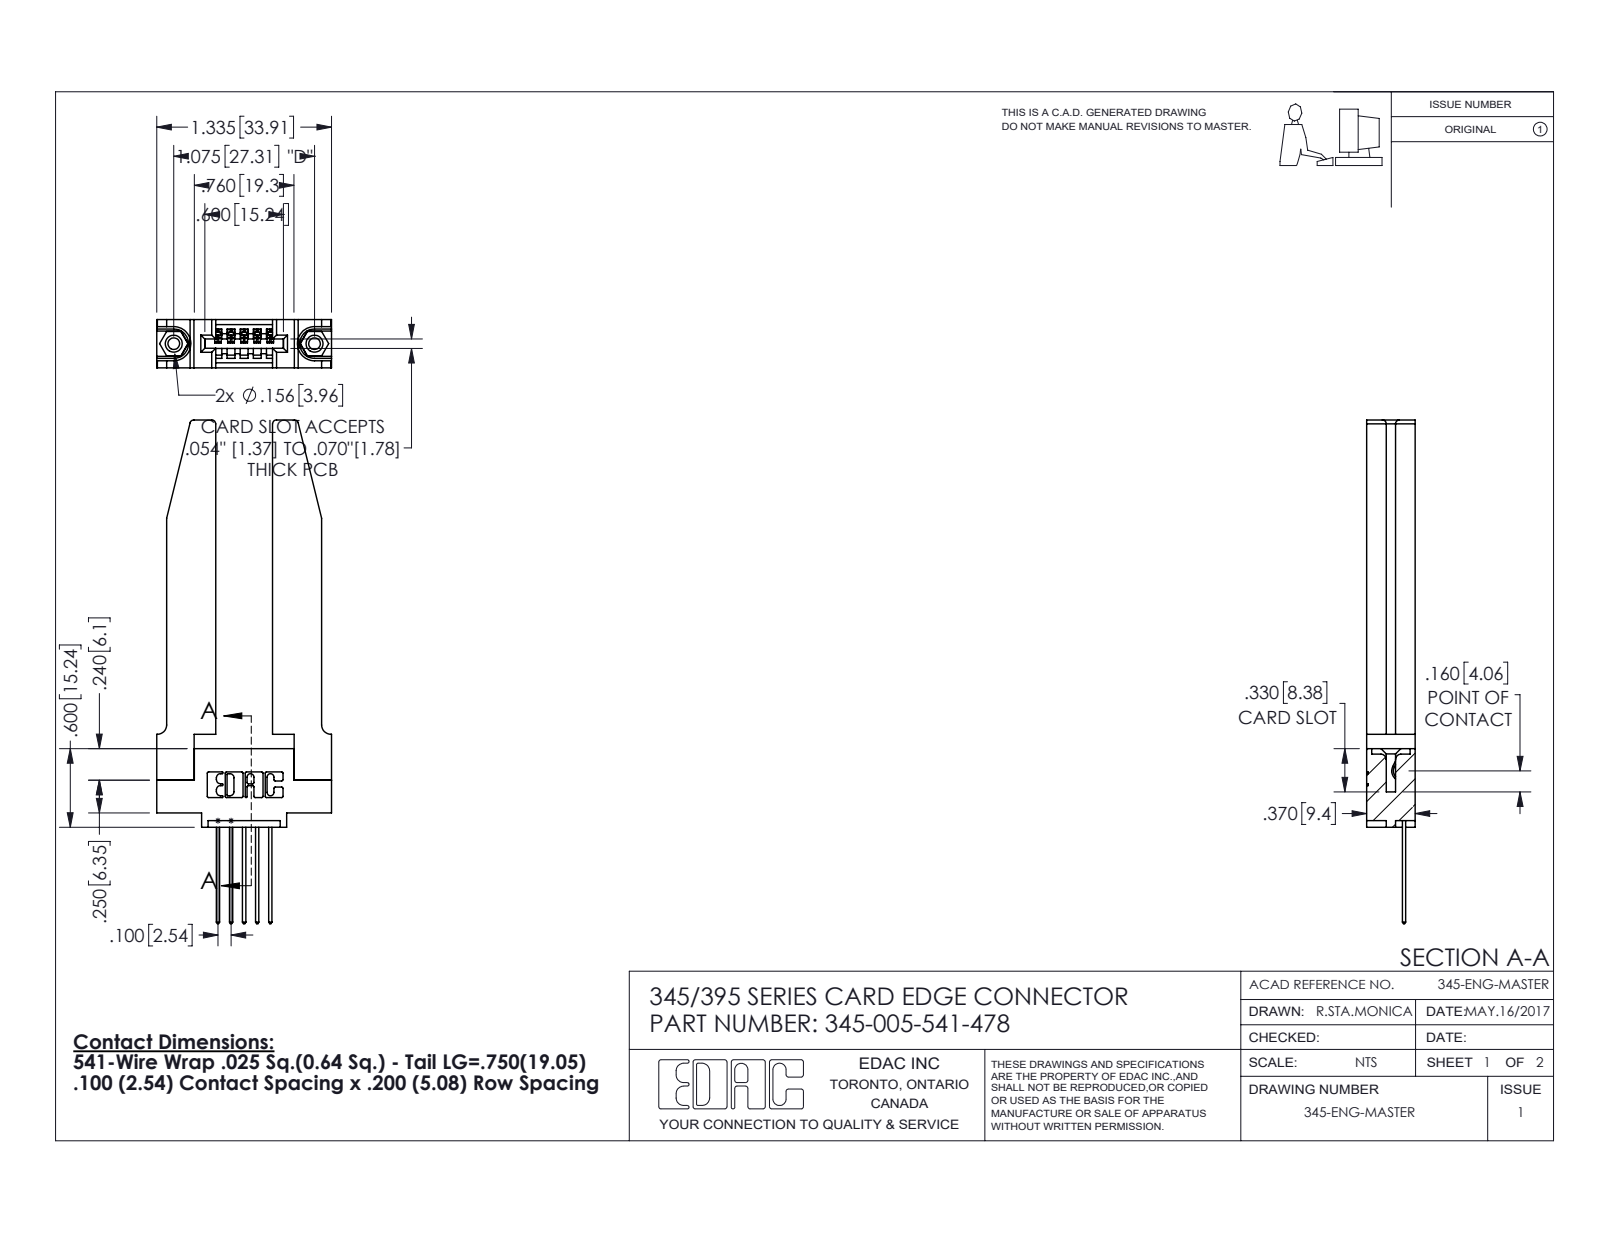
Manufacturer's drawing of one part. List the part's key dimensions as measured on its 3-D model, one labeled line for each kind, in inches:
Part name (STEP PRODUCT): 345 Part_0.110 Offset - 0.156 Dia-TH; 345-250-001_345-250-001-102; 345-220-078_345-220-078; 345-292-001_345-293-141 (+1 more)
STEP written by: SolidWorks 2016 (CONFIG_CONTROL_DESIGN)
Units: inches
Bodies: 10 solids, 654 faces (426 planar, 176 cylindrical, 52 other)
Overall size (bounding box): 3.847 × 1.336 × 0.37
Volume: 0.649 in³ · Surface area: 16.01 in²
Round holes (diameter × count): ⌀0.089 ×2, ⌀0.125 ×2, ⌀0.156 ×2, ⌀0.064 ×1
Round bosses / shafts (diameter × count): ⌀0.155 ×2
Partial cylindrical surfaces — rounded edges, fillets, slot ends (radius × count): R0.01 ×22, R0.006 ×10, R0.01 ×10, R0.03 ×8, R0.007 ×6, R0.031 ×6, R0.026 ×3, R0.031 ×2
Main face-to-face distances: 0.37, 0.15, 0.22, 0.435, 0.148, 0.072, 0.298, 0.077, 0.2, 0.071
Hole centre spacings: 0.27, 0.847, 1.075
